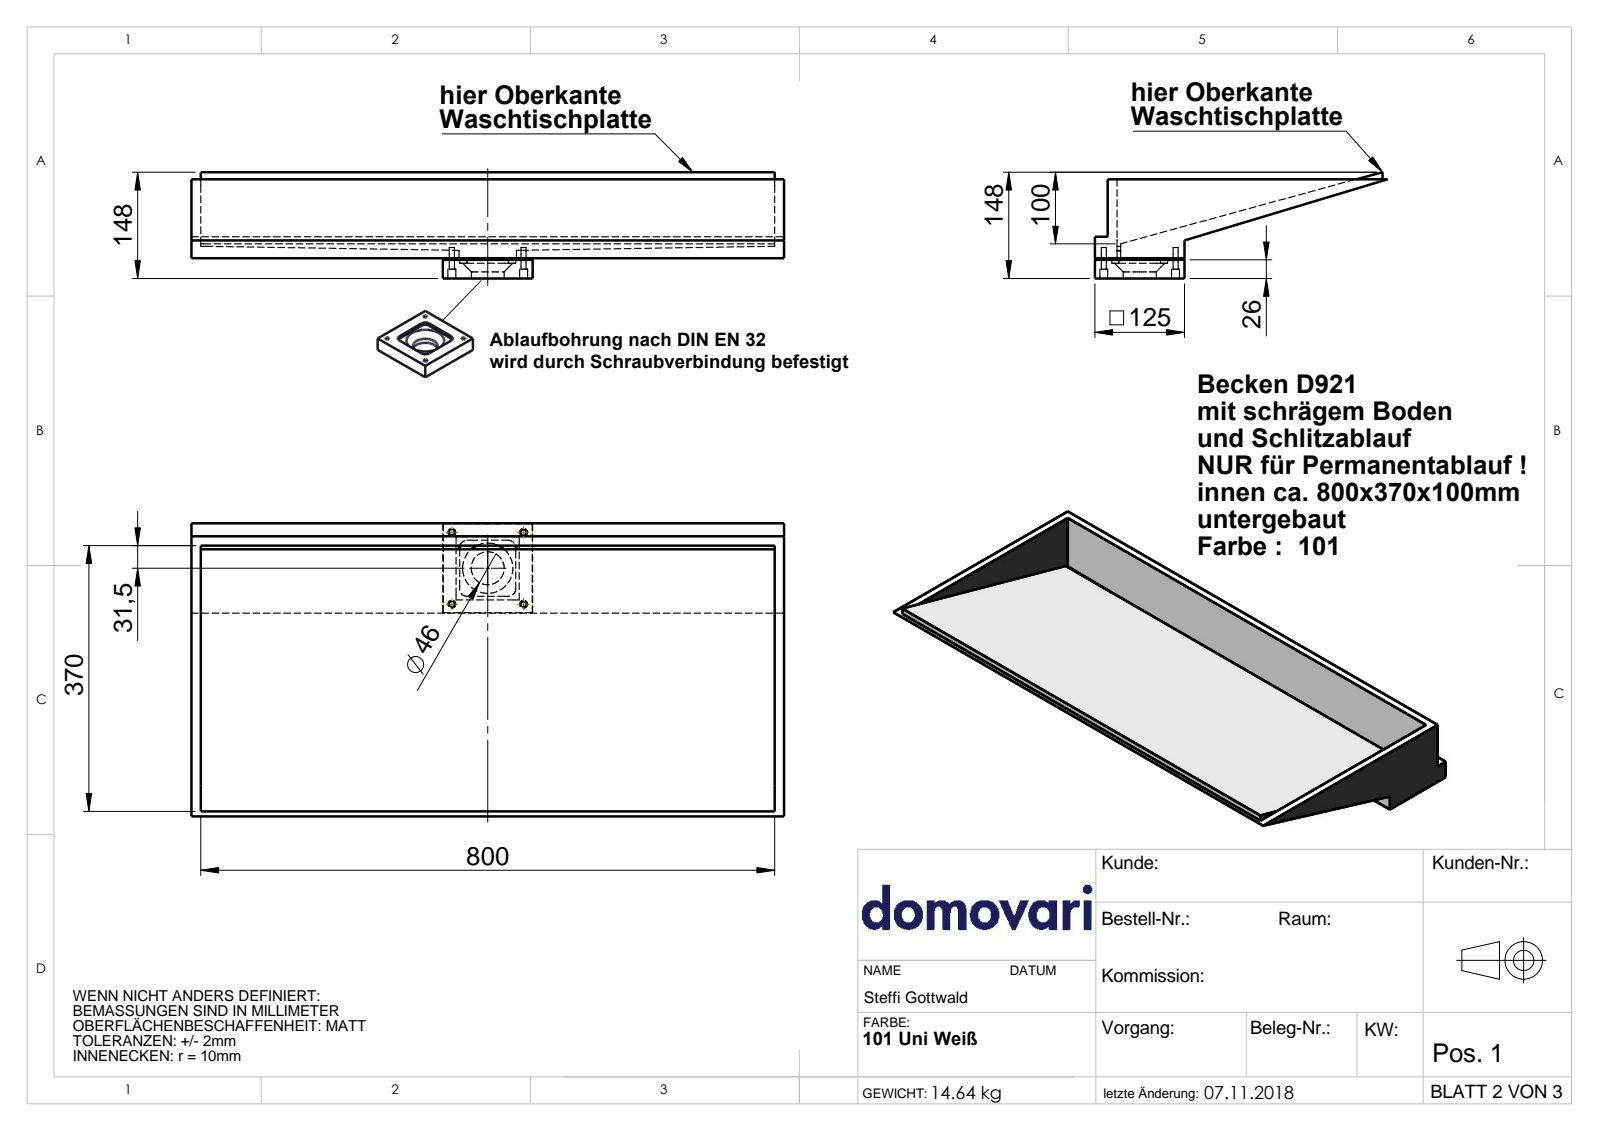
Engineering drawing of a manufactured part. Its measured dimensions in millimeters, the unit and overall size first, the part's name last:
Units: millimetres
Overall size (bounding box): 826 × 408 × 148
Round holes (diameter × count): ⌀7 ×4, ⌀8 ×4, ⌀11 ×4, ⌀46 ×1
Partial cylindrical surfaces — rounded edges, fillets, slot ends (radius × count): R0.5 ×4, R10 ×4
Main face-to-face distances: 13, 18, 813, 31, 125, 110, 826, 107, 94, 2
Hole centre spacings: 70.71, 100, 141.42
Volume: 8 367 000 mm³ · Surface area: 1 043 000 mm²
Bodies: 3 solids, 94 faces (50 planar, 42 cylindrical, 2 other)
Part name (STEP PRODUCT): D921
STEP written by: SolidWorks 2017 (AUTOMOTIVE_DESIGN)
